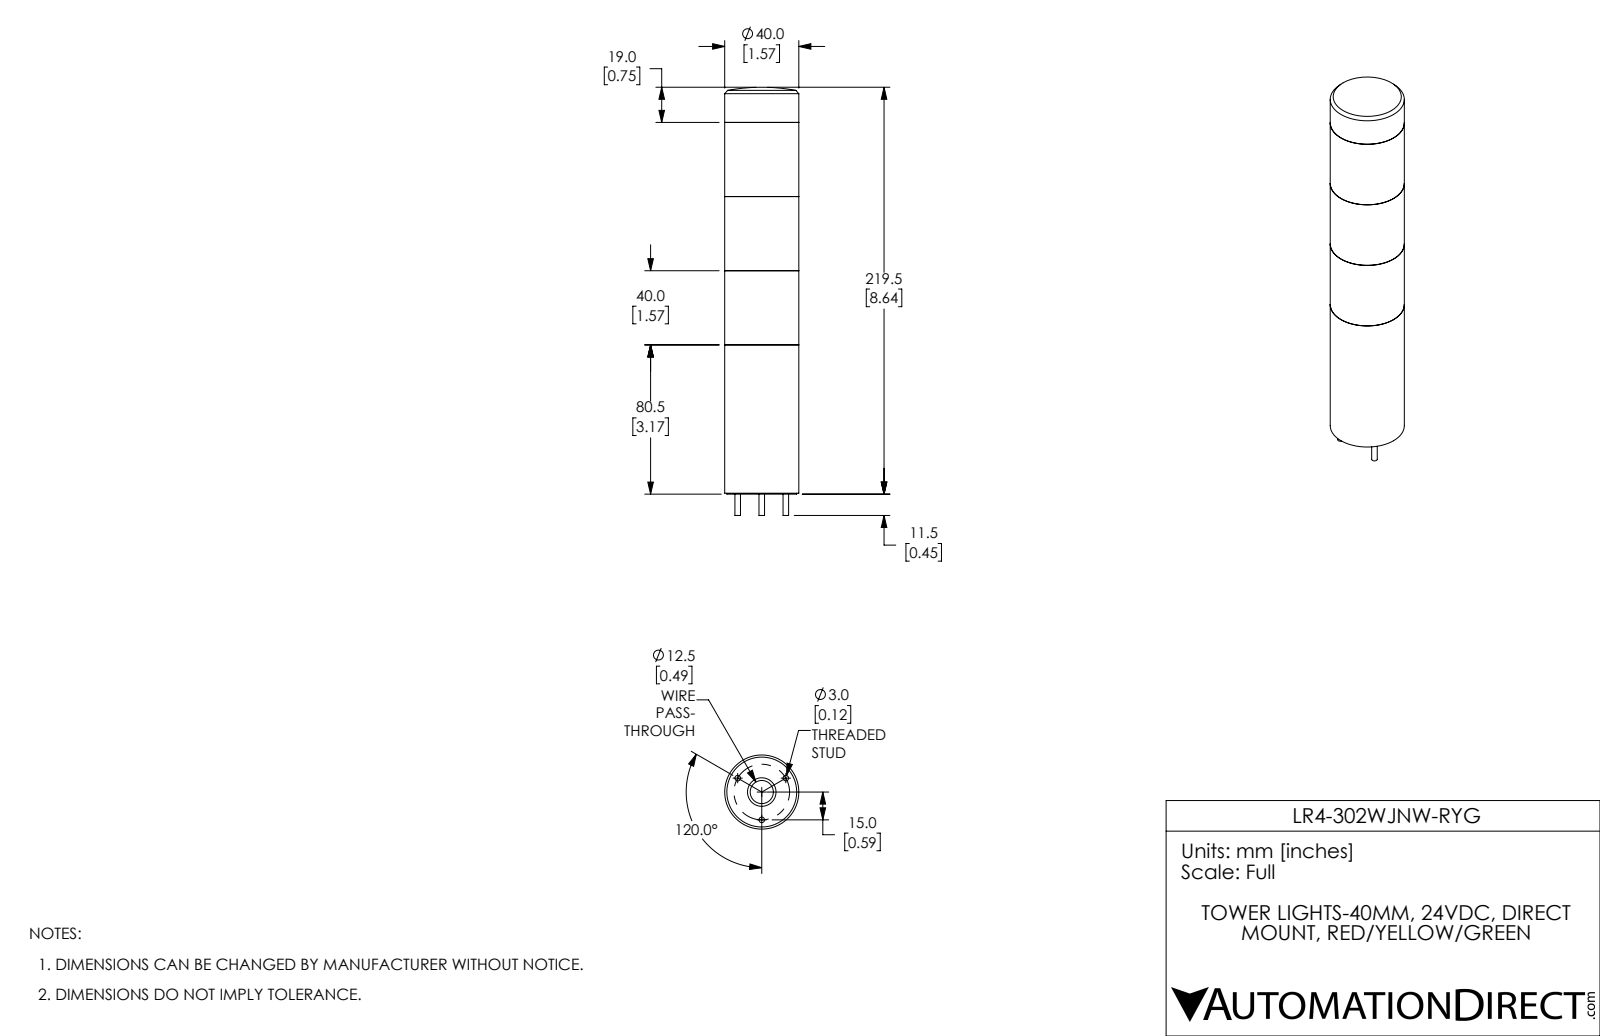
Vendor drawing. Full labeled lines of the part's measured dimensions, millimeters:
Part name (STEP PRODUCT): LR4-302WJNW-RYG
STEP written by: SolidWorks 2017 (AUTOMOTIVE_DESIGN)
Units: millimetres
Bodies: 5 solids, 88 faces (31 planar, 54 cylindrical, 3 other)
Overall size (bounding box): 231 × 40 × 40
Volume: 274 000 mm³ · Surface area: 49 580 mm²
Round holes (diameter × count): ⌀12.5 ×1, ⌀15.4 ×1, ⌀34.7 ×1, ⌀35.2 ×1, ⌀37.1 ×1, ⌀37.2 ×1
Round bosses / shafts (diameter × count): ⌀3 ×3, ⌀40 ×1, ⌀37.7 ×1
Main face-to-face distances: 40, 80, 120, 10.3, 50.3, 29.7, 3.2, 7.1, 90.8, 130.8
